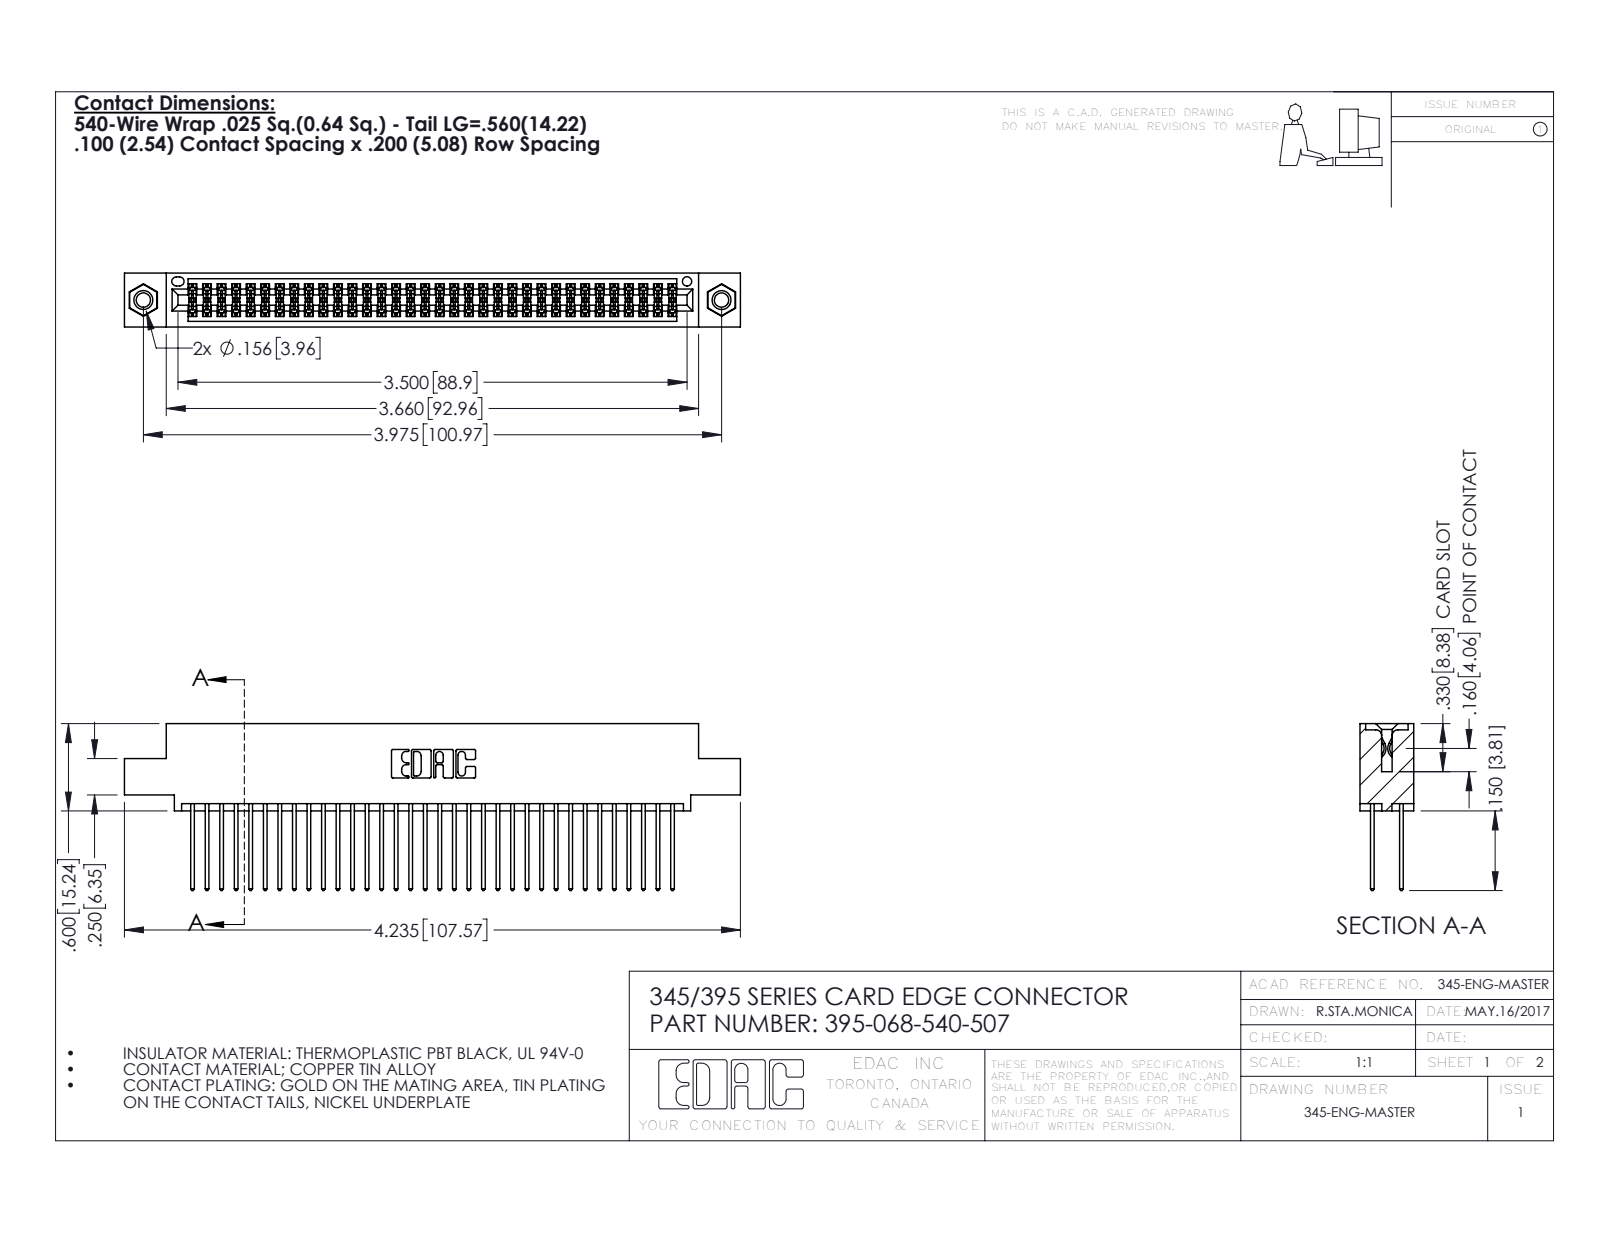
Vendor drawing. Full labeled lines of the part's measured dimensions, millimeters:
Part name (STEP PRODUCT): 395-068-540-507; 345-250-001_345-250-005-103; 345-292-001_345-293-140; 345 Part_0.110 Offset - 0.156 Dia-TI
STEP written by: SolidWorks 2016 (CONFIG_CONTROL_DESIGN)
Units: millimetres
Bodies: 71 solids, 3590 faces (2360 planar, 1214 cylindrical, 16 other)
Overall size (bounding box): 107.6 × 29.1 × 9.4
Volume: 10 600 mm³ · Surface area: 16 750 mm²
Round holes (diameter × count): ⌀2.5 ×2, ⌀3.2 ×2, ⌀4 ×2, ⌀1.6 ×1
Round bosses / shafts (diameter × count): ⌀3.9 ×2
Partial cylindrical surfaces — rounded edges, fillets, slot ends (radius × count): R0.2 ×102, R0.3 ×68, R0.3 ×22, R0.2 ×6, R0.8 ×6, R0.7 ×3, R0.4 ×2, R0.5 ×2
Main face-to-face distances: 1.8, 7.6, 5.1, 2.5, 6.9, 0.6, 9.4, 5.7, 4.4, 3.8
Hole centre spacings: 6.9, 95, 101
